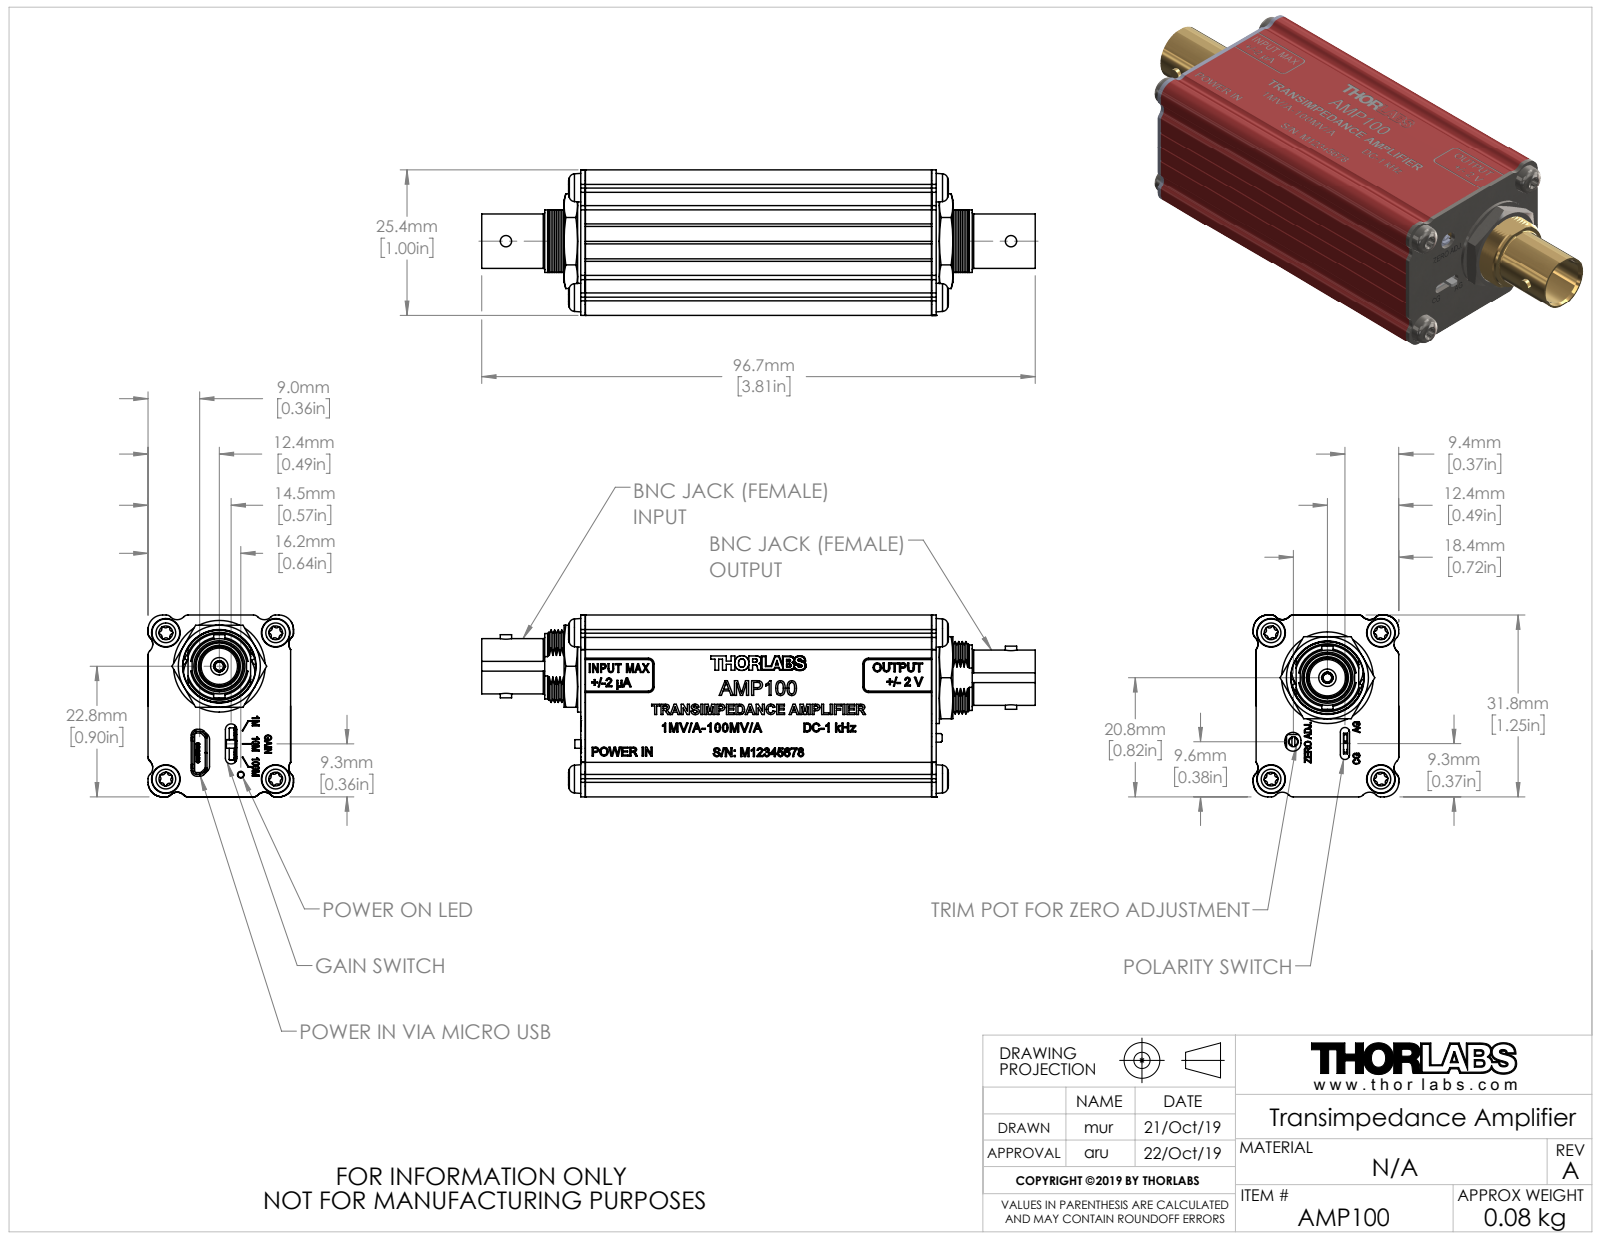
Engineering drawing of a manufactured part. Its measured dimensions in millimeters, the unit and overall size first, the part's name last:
Units: millimetres
Overall size (bounding box): 96.65 × 31.75 × 25.4
Round holes (diameter × count): ⌀3.5 ×8, ⌀0.2 ×4, ⌀0.6 ×4, ⌀0.85 ×2, ⌀0.9 ×2, ⌀1.19 ×2, ⌀1.49 ×2, ⌀1.93 ×2, ⌀4.04 ×2, ⌀6.93 ×2, ⌀8.86 ×2, ⌀12.7 ×2
Round bosses / shafts (diameter × count): ⌀0.46 ×6, ⌀2.5 ×4, ⌀2.22 ×4, ⌀16 ×2, ⌀11.43 ×2, ⌀10.46 ×2, ⌀9.65 ×2, ⌀6.91 ×2
Partial cylindrical surfaces — rounded edges, fillets, slot ends (radius × count): R0.24 ×48, R0.42 ×48, R0.2 ×40, R0.1 ×37, R0.15 ×23, R1.02 ×22, R0.25 ×14, R0.4 ×12
Main face-to-face distances: 1.27, 3.05, 1.64, 0.8, 9.14, 6.1, 12.19, 17.91, 61.28, 4.32
Hole centre spacings: 2, 19.18, 1.11, 14.86, 25.53, 31.93, 5, 11.08
Bodies: 0 solids, 4717 faces (3144 planar, 665 cylindrical, 908 other)
Part name (STEP PRODUCT): 19.12.02_AMP100 WEB
STEP written by: SolidWorks 2018 (AUTOMOTIVE_DESIGN)
